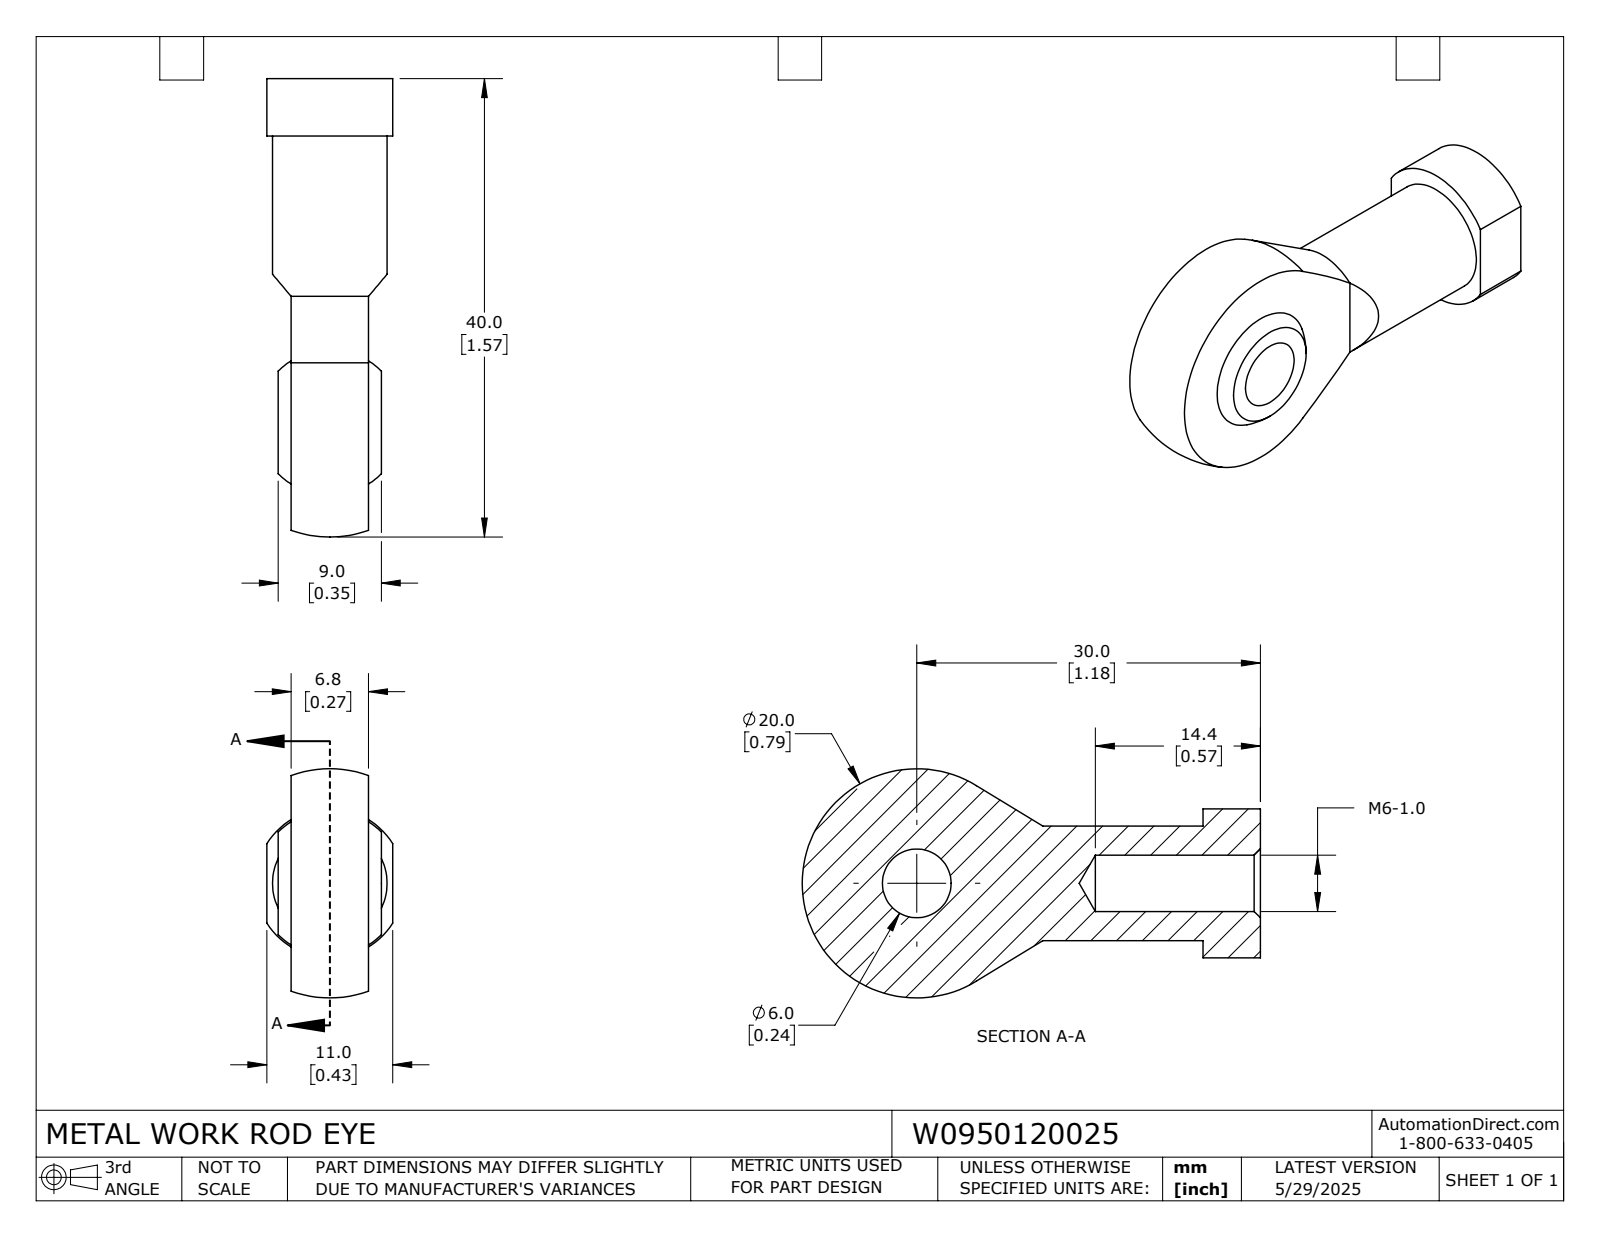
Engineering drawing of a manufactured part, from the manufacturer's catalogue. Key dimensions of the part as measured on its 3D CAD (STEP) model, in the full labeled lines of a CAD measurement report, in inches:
Part name (STEP PRODUCT): W0950120025
STEP written by: SolidWorks 2024 (CONFIG_CONTROL_DESIGN)
Units: inches
Bodies: 1 solid, 28 faces (10 planar, 8 cylindrical, 10 other)
Overall size (bounding box): 1.575 × 0.787 × 0.433
Volume: 0.215 in³ · Surface area: 3.354 in²
Round holes (diameter × count): ⌀0.194 ×1, ⌀0.236 ×1
Round bosses / shafts (diameter × count): ⌀0.394 ×1
Partial cylindrical surfaces — rounded edges, fillets, slot ends (radius × count): R0.256 ×1
Main face-to-face distances: 0.266, 0.044, 0.31, 0.039, 0.083, 0.35, 0.394, 0.197, 0.354, 0.433
